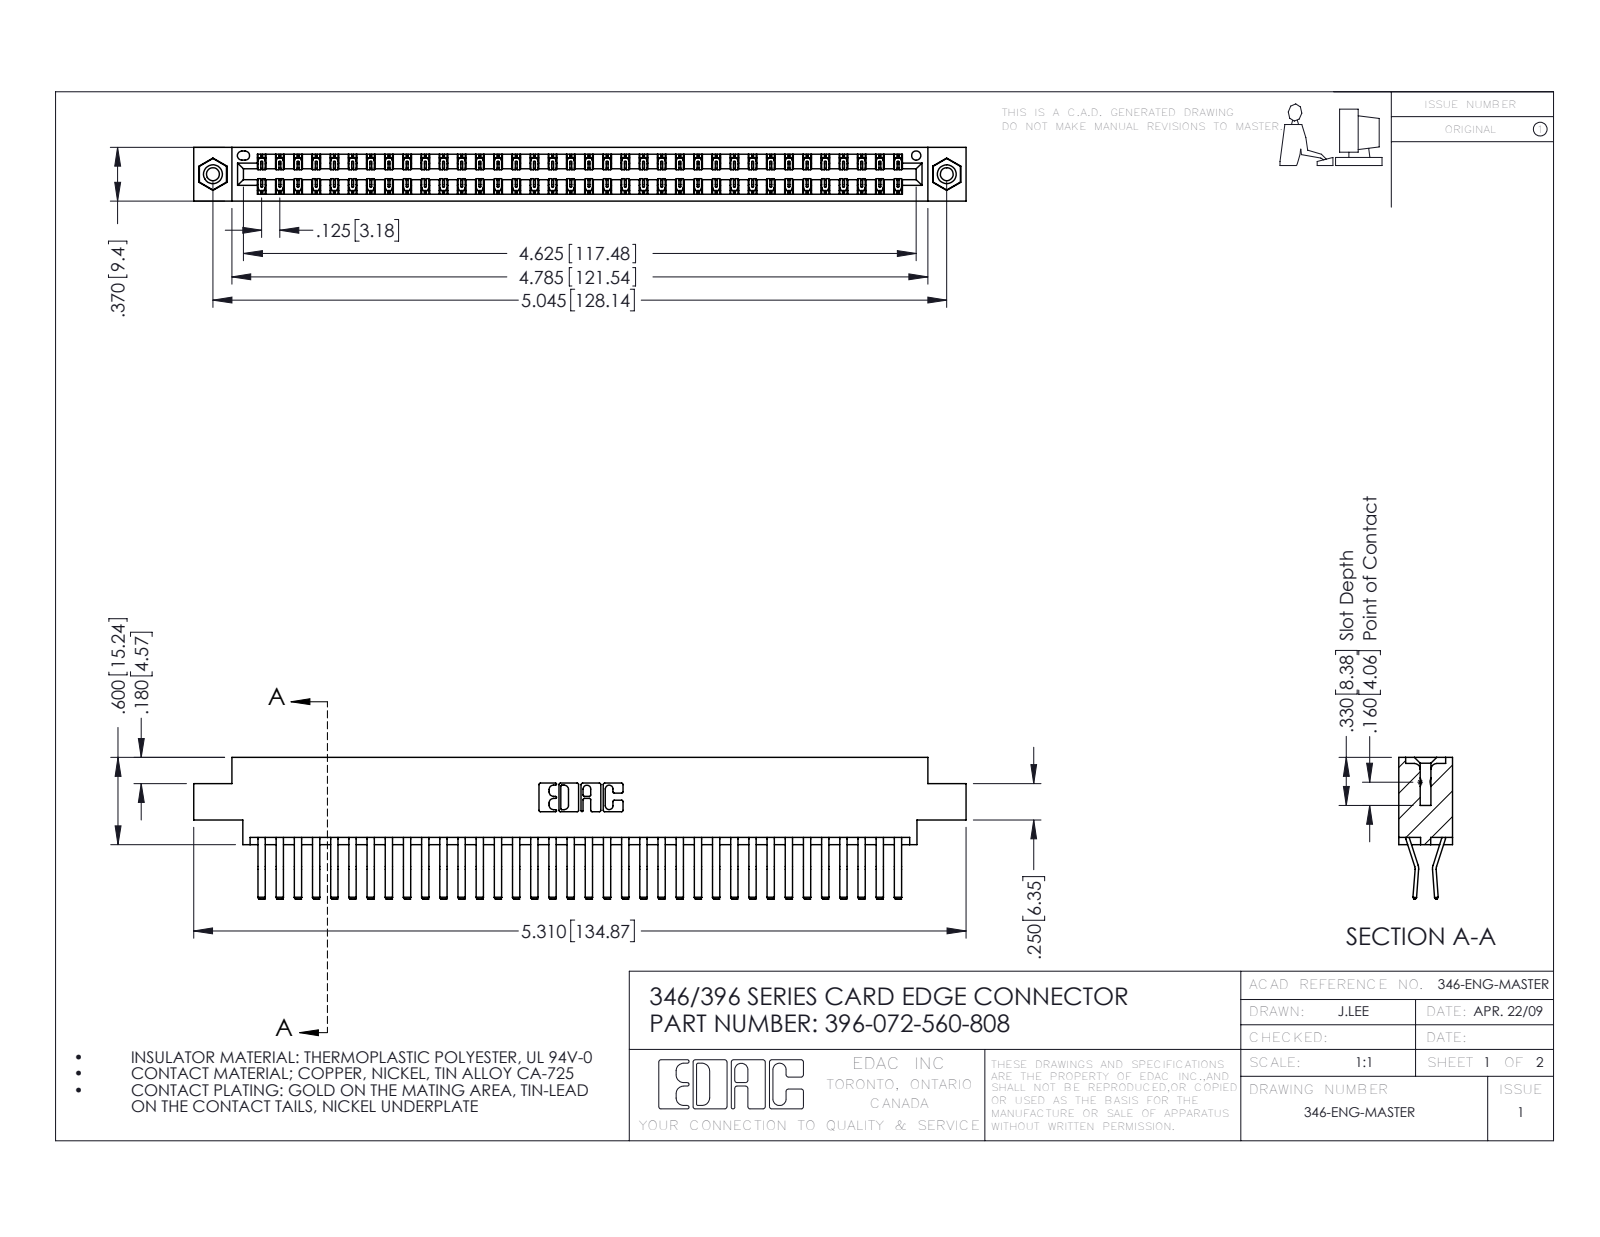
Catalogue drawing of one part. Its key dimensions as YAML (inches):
part_name: "345-250-001_345-250-003-102; 345-292-001_560 Tail; 346 Part_0.170 Offset - 0.156 Dia-TI; 396-072-560-808"
step_written_by: "SolidWorks 2016 (CONFIG_CONTROL_DESIGN)"
units: inches
bodies: {solids: 75, faces: 4074, planar: 2632, cylindrical: 1426, other: 16}
overall_size: [5.31, 0.975, 0.37]
volume: 0.819
surface_area: 30.7
round_holes:
  - {diameter: 0.089, count: 2}
  - {diameter: 0.125, count: 2}
  - {diameter: 0.156, count: 2}
  - {diameter: 0.064, count: 1}
round_bosses_or_shafts:
  - {diameter: 0.155, count: 2}
partial_cylinders:
  - {radius: 0.006, count: 108}
  - {radius: 0.01, count: 22}
  - {radius: 0.007, count: 6}
  - {radius: 0.031, count: 6}
  - {radius: 0.026, count: 3}
  - {radius: 0.01, count: 2}
  - {radius: 0.014, count: 2}
  - {radius: 0.022, count: 2}
face_to_face_distances: [0.048, 0.322, 0.37, 0.025, 0.25, 0.072, 0.298, 0.275, 0.222, 0.148]
hole_center_spacings: [0.246, 4.836, 5.045]
